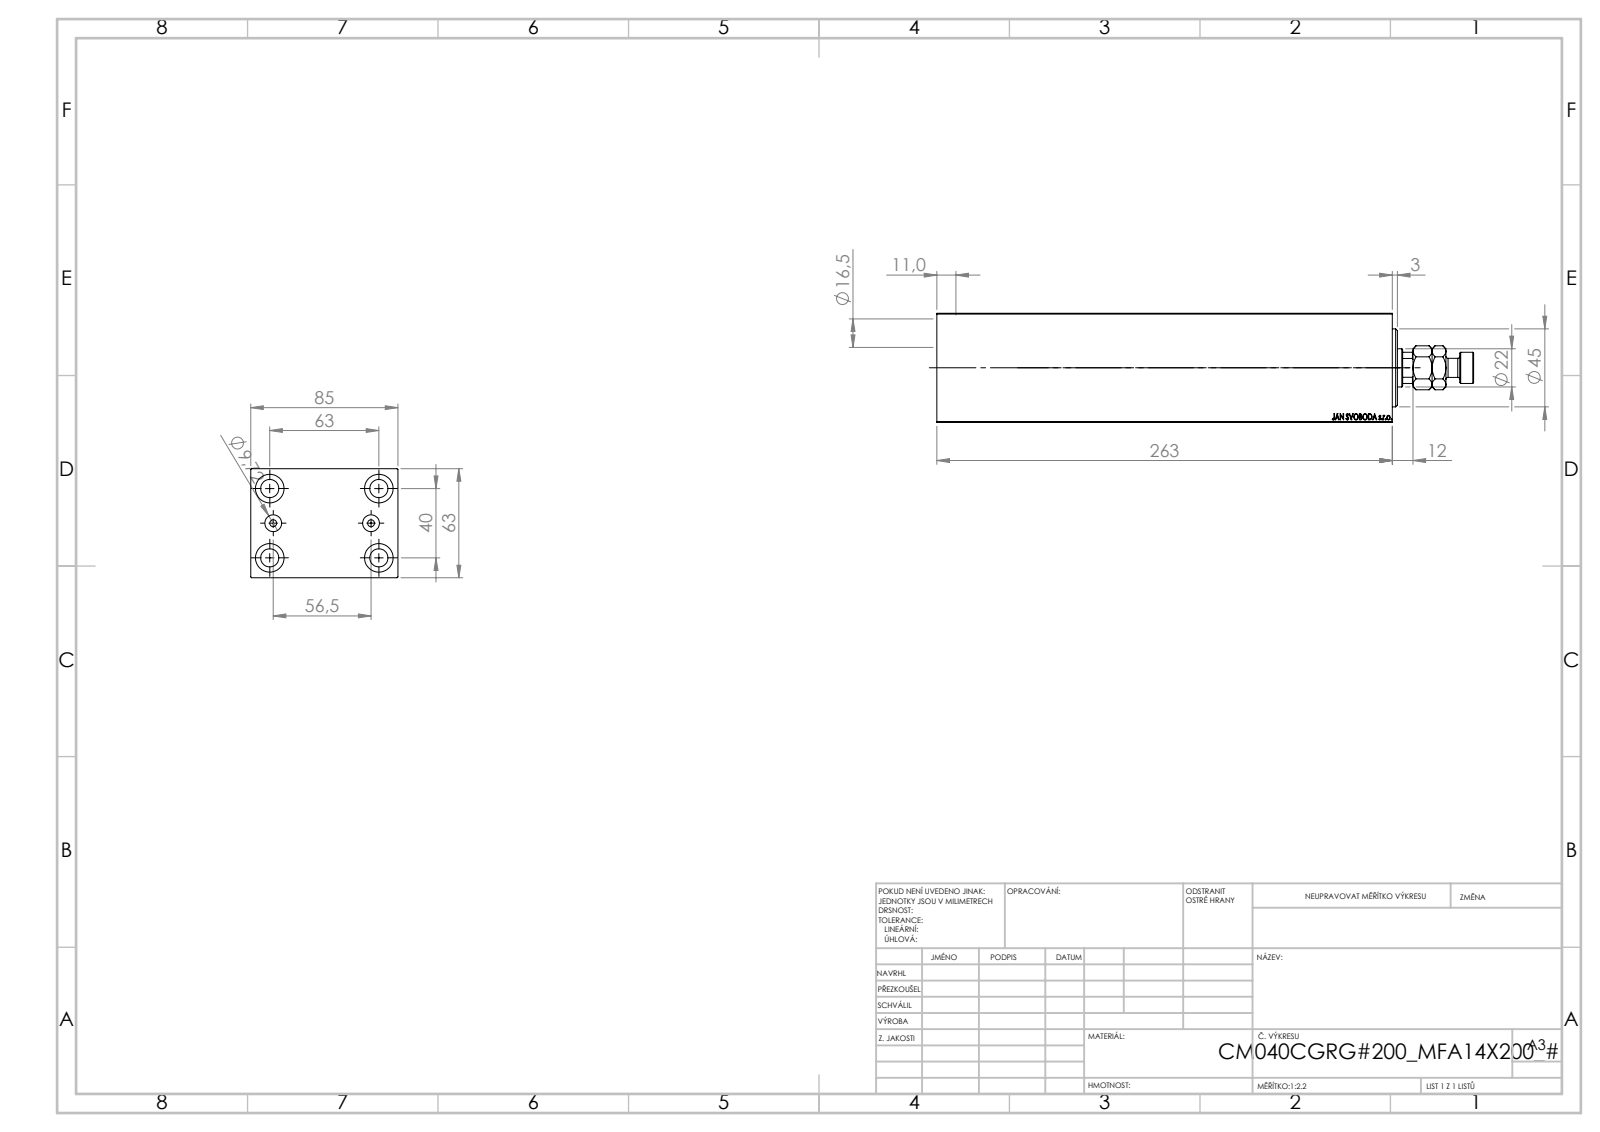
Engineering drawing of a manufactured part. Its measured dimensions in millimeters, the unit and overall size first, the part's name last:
Units: millimetres
Overall size (bounding box): 310 × 85 × 63
Round holes (diameter × count): ⌀10.5 ×4, ⌀16.5 ×4, ⌀4 ×2, ⌀9.72 ×2, ⌀12.5 ×1, ⌀22 ×1, ⌀25.5 ×1, ⌀40 ×1, ⌀42 ×1, ⌀45 ×1
Round bosses / shafts (diameter × count): ⌀18 ×1, ⌀11 ×1
Partial cylindrical surfaces — rounded edges, fillets, slot ends (radius × count): R10.5 ×1
Main face-to-face distances: 63, 85, 12, 251, 263, 1, 239, 11, 252, 240
Hole centre spacings: 37.31, 20.1, 20.5, 40, 61.82, 63, 64.2, 74.63
Volume: 1 138 000 mm³ · Surface area: 194 768 mm²
Bodies: 4 solids, 910 faces (424 planar, 60 cylindrical, 426 other)
Part name (STEP PRODUCT): MFA; V450CM_C_VCP; V450CM_VC_B; V450CM_C_Body
STEP written by: SolidWorks 2019 (CONFIG_CONTROL_DESIGN)
